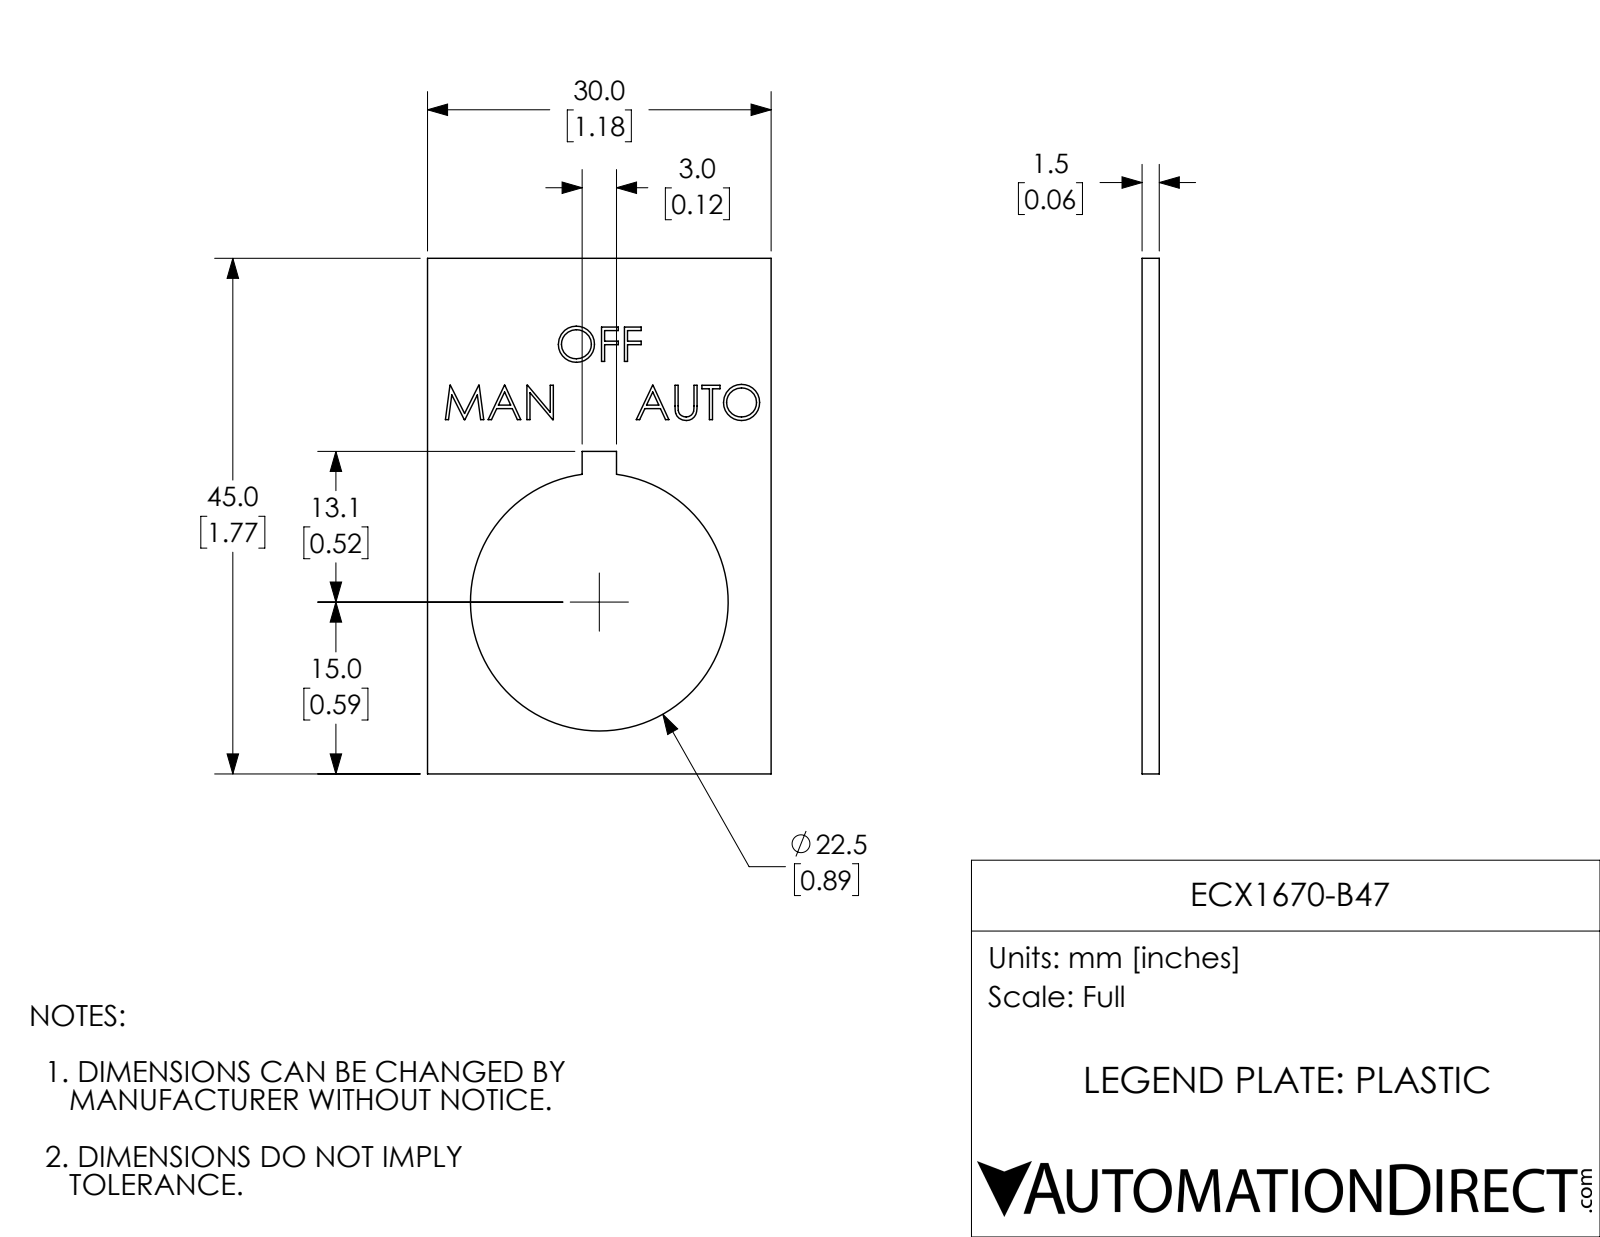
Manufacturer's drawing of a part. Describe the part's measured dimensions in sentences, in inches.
The part is named "ECX1670-B47". Its 3-D file was written by "SolidWorks 2017 (AUTOMOTIVE_DESIGN)". It is 1 solid with 128 faces: 102 planar, 3 cylindrical and 23 other. Overall it measures 1.772 by 1.181 by 0.059 inches. Its volume is 0.087 cubic inches and its surface area 3.463 square inches. Round holes: 1 of diameter 0.886. The main face-to-face distances are 0.059, 1.181, 1.772, 0.058, 0.531, 0.65, 1.108, 0.663, 0.118, 0.012.
